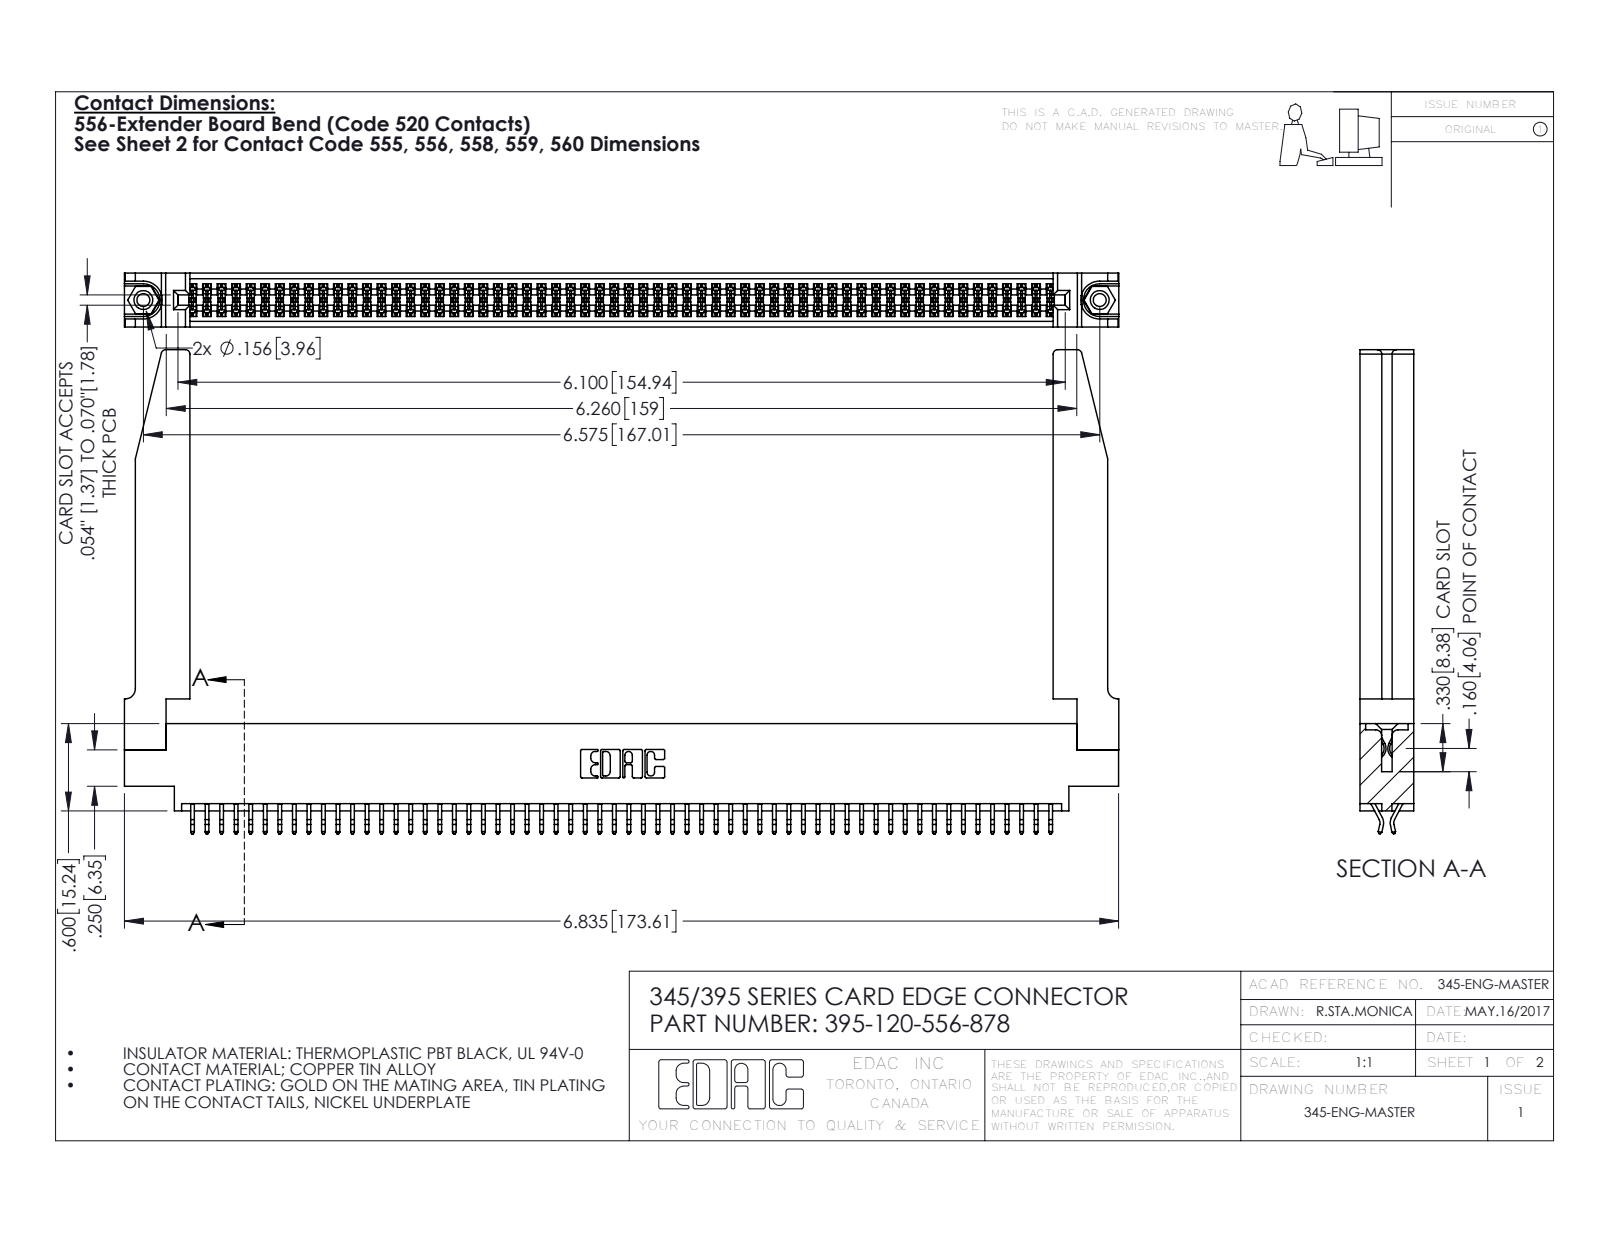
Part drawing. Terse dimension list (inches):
name: 345-250-001_345-250-001-102; 345-292-001_556 Tail; 345 Part_0.170 Offset - 0.156 Dia-TH; 395-120-556-878 (+1 more)
written by: SolidWorks 2016 (CONFIG_CONTROL_DESIGN)
unit: in
bodies: 125 solids, 7084 faces (4666 planar, 2366 cylindrical, 52 other)
size: 6.836 × 3.327 × 0.37
volume: 1.506 in³; area: 49.96 in²
holes: 2× ⌀0.089, 2× ⌀0.125, 2× ⌀0.156, 1× ⌀0.064
bosses: 2× ⌀0.155
rounds: 180× R0.006, 22× R0.01, 8× R0.03, 6× R0.007, 6× R0.031, 3× R0.026, 2× R0.01, 2× R0.014
face distances: 0.072, 0.37, 0.298, 0.025, 0.098, 0.272, 0.2, 0.225, 0.175, 0.148
hole spacings: 0.27, 6.339, 6.575
